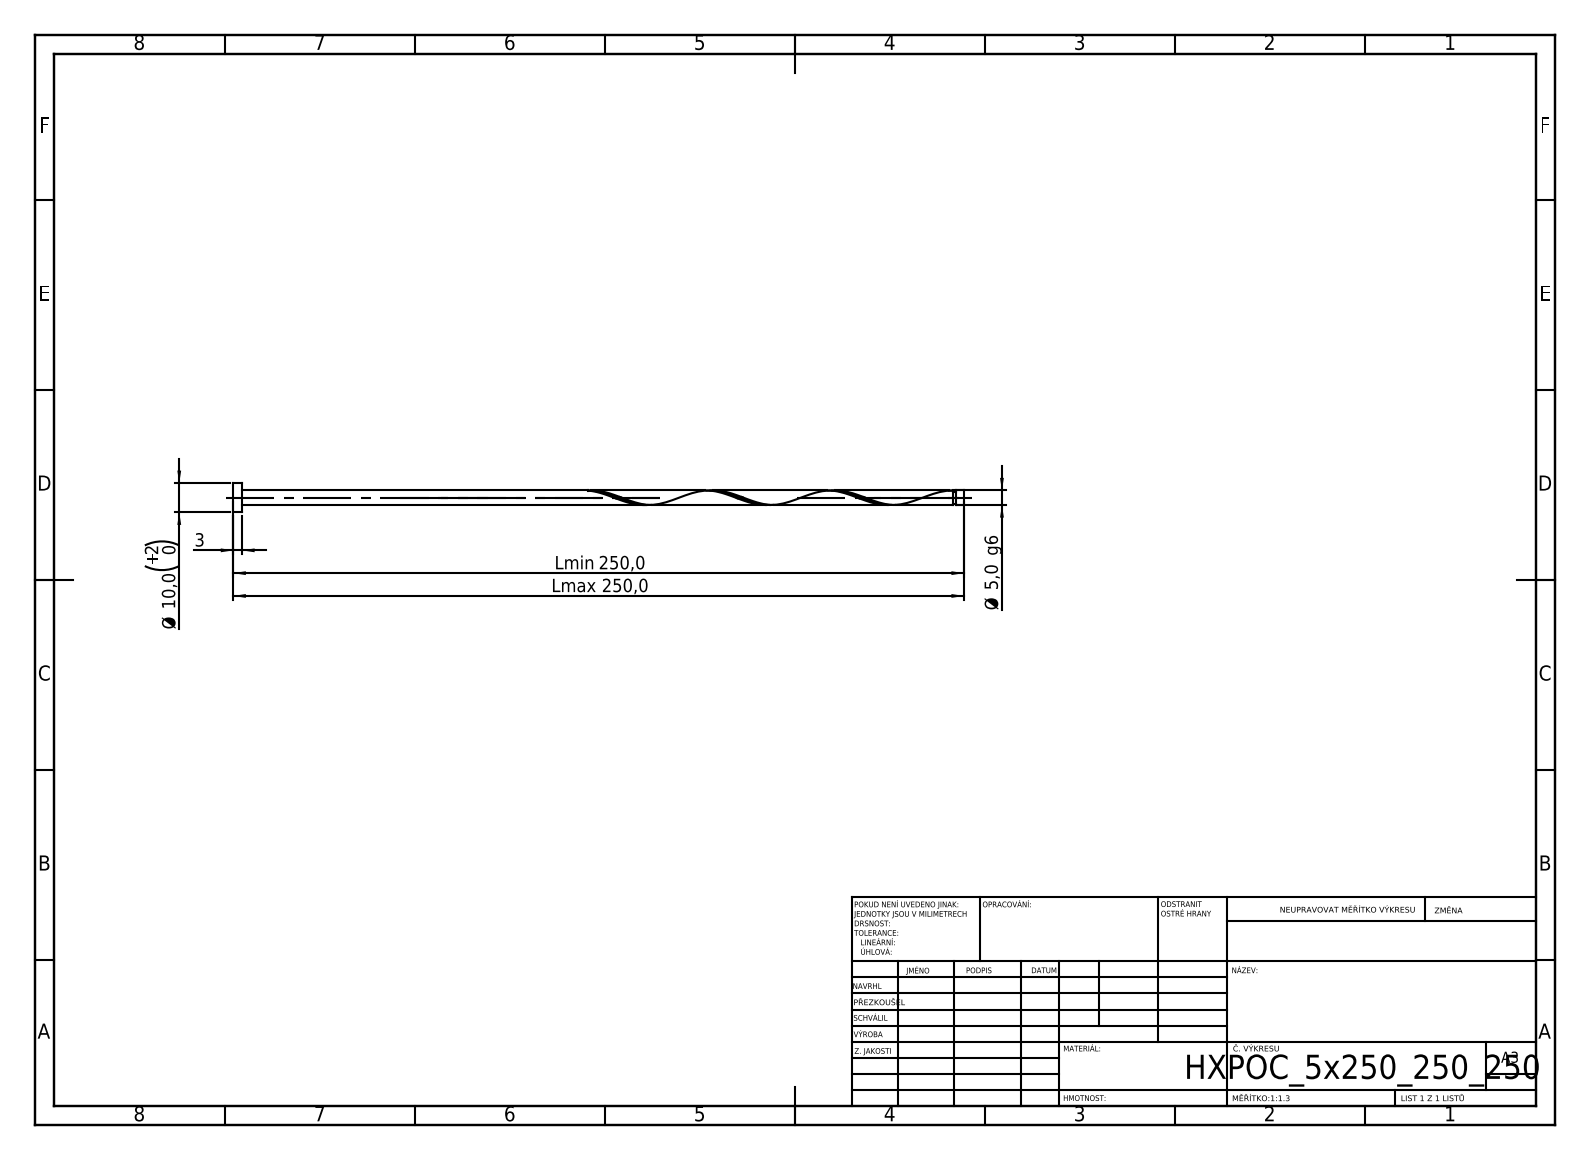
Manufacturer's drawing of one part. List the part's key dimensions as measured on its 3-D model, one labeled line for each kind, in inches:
STEP written by: SolidWorks 2019 (CONFIG_CONTROL_DESIGN)
Units: inches
Bodies: 1 solid, 21 faces (6 planar, 14 cylindrical, 1 other)
Overall size (bounding box): 9.843 × 0.394 × 0.394
Volume: 0.307 in³ · Surface area: 6.521 in²
Round bosses / shafts (diameter × count): ⌀0.394 ×1, ⌀0.197 ×1, ⌀0.157 ×1
Main face-to-face distances: 0.118, 9.843, 9.724, 9.733, 9.615, 0.109, 9.694, 9.576, 0.039, 0.149
